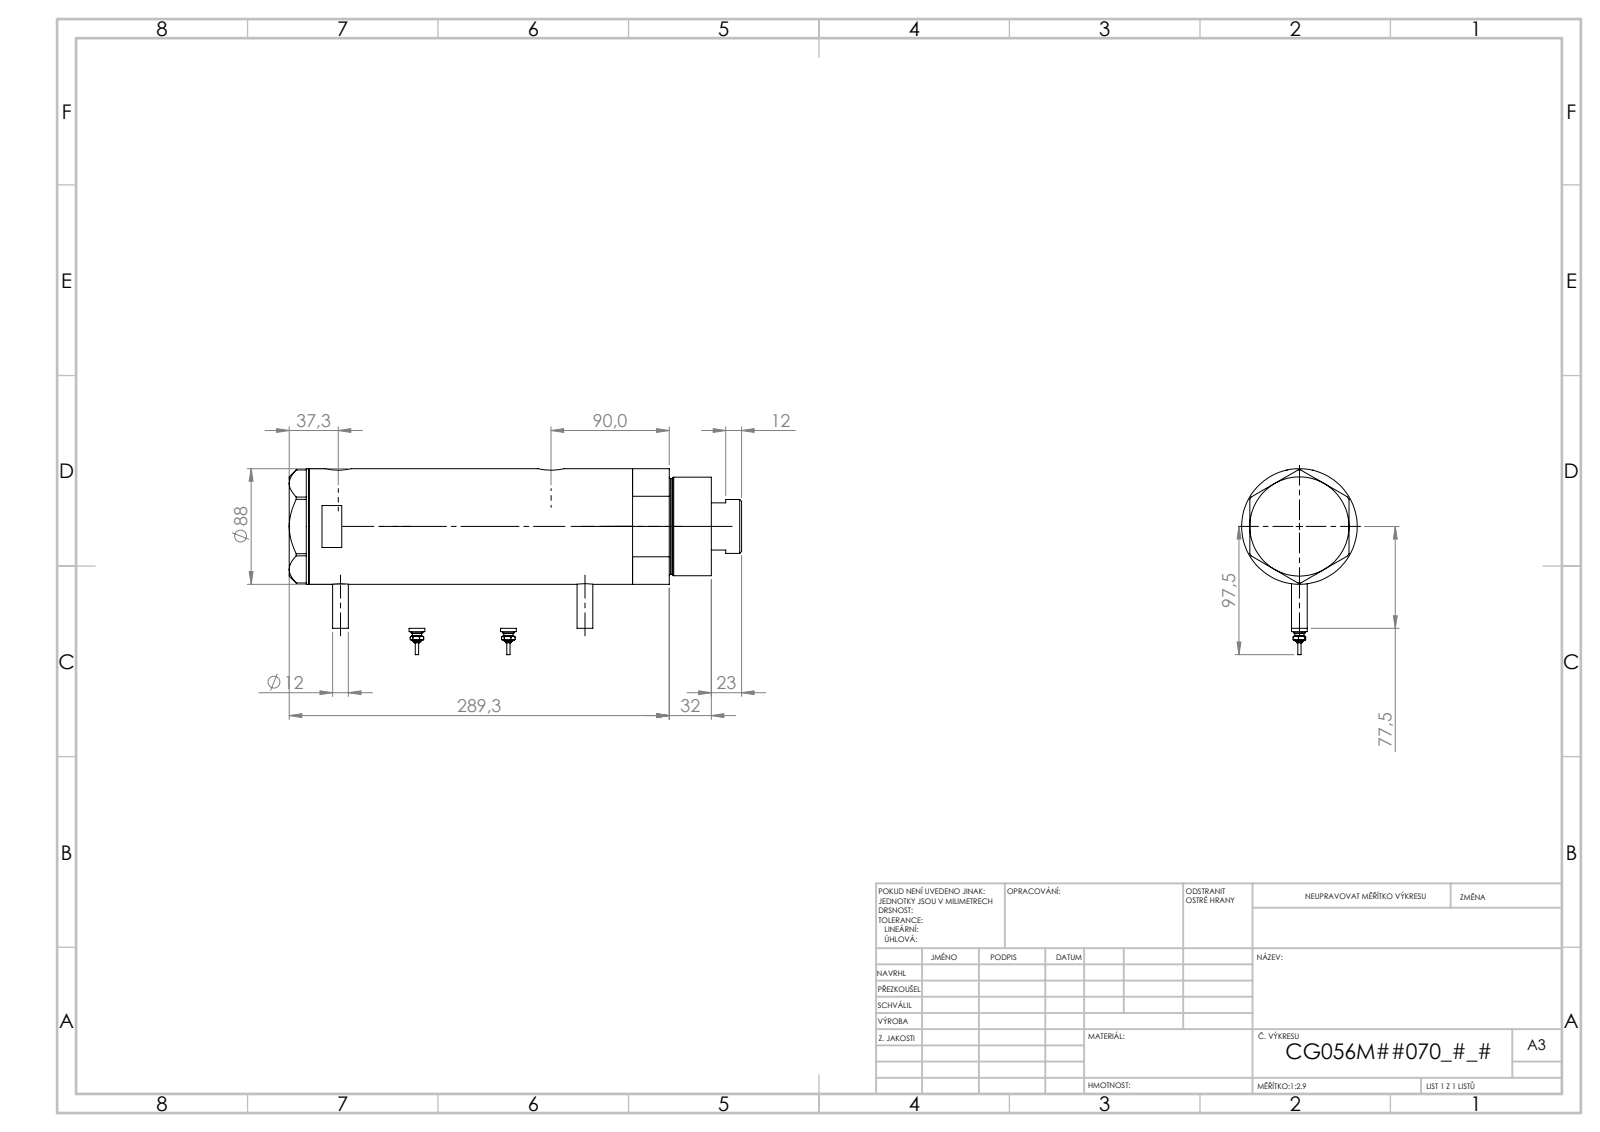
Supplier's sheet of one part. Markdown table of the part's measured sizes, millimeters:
| quantity | value |
| --- | --- |
| part name | V270CG_SWITCH; V270CG_VC; V270CG_FRONT; V270CG_BACK (+1 more) |
| STEP written by | SolidWorks 2019 (CONFIG_CONTROL_DESIGN) |
| units | millimeters |
| bodies | 6 solids, 232 faces (81 planar, 77 cylindrical, 74 other) |
| overall size | 294.47 × 120.3 × 88 |
| volume | 1 515 000 mm³ |
| surface area | 223 110 mm² |
| round holes (diameter × count) | 5 × 2, 12.5 × 2, 13.16 × 2, 20 × 2, 14.5 × 1, 42 × 1, 43.5 × 1, 56 × 1, 60 × 1, 80 × 1 |
| round bosses / shafts (diameter × count) | 12 × 2, 9 × 2, 7 × 2, 4.34 × 2, 2.4 × 2, 88 × 1, 75 × 1, 73 × 1 |
| main face-to-face distances | 144.4, 26, 118.4, 15, 41, 159.4, 256.47, 271.47, 230.47, 112.07 |
| hole center spacings | 1.7, 25.8, 120.3, 122, 146.1, 147.8 |
